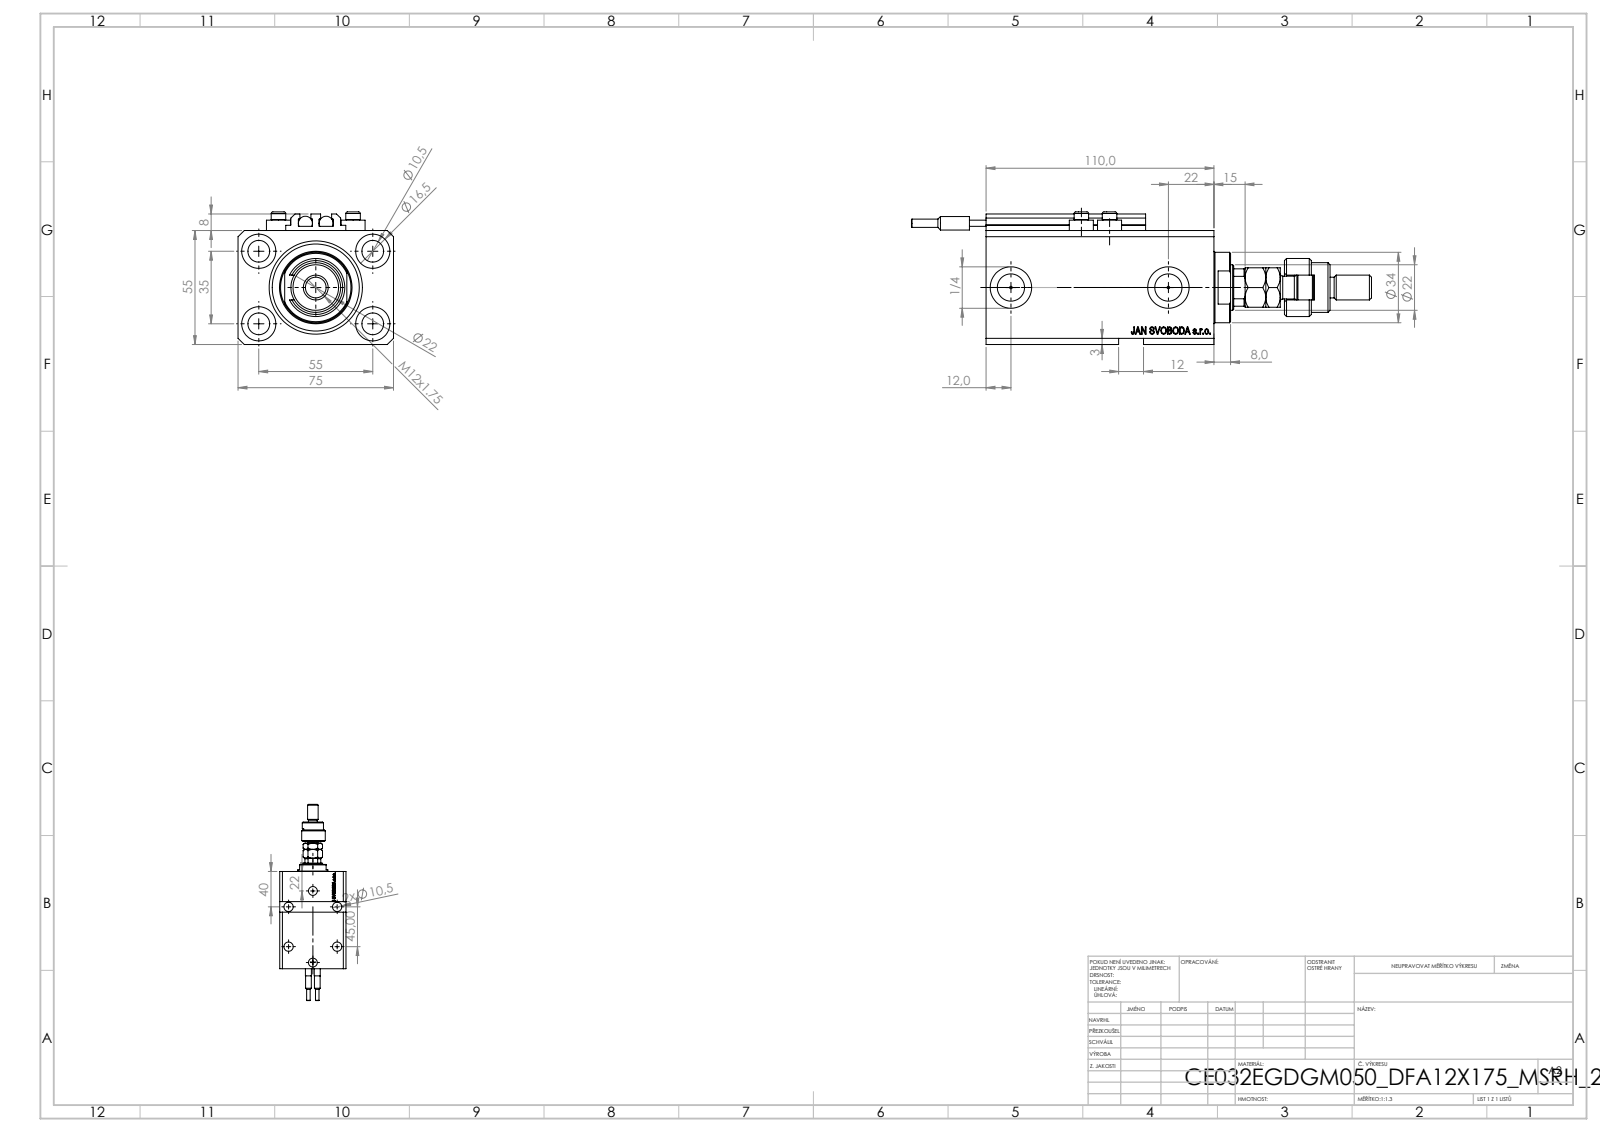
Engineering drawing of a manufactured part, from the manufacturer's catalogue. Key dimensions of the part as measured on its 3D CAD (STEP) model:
Part name (STEP PRODUCT): V250CE_VC_E; FEMALE_PART_FOR_DFA; ALLEN BOLT V250CE; V250CE_C_VCP (+3 more)
STEP written by: SolidWorks 2019 (CONFIG_CONTROL_DESIGN)
Units: millimetres
Bodies: 12 solids, 1237 faces (578 planar, 183 cylindrical, 476 other)
Overall size (bounding box): 222 × 75 × 64
Volume: 399 171 mm³ · Surface area: 106 662 mm²
Round holes (diameter × count): ⌀10.5 ×9, ⌀1.25 ×4, ⌀4 ×4, ⌀16.5 ×4, ⌀10 ×2, ⌀13.16 ×2, ⌀20 ×2, ⌀22 ×1, ⌀32 ×1, ⌀45 ×1
Round bosses / shafts (diameter × count): ⌀11.6 ×4, ⌀7 ×4, ⌀6.8 ×2, ⌀6.5 ×2, ⌀4 ×2, ⌀34 ×1, ⌀28 ×1, ⌀24 ×1
Partial cylindrical surfaces — rounded edges, fillets, slot ends (radius × count): R0.2 ×10, R9.75 ×1, R10.5 ×1
Main face-to-face distances: 55, 75, 15, 3, 110, 57, 95, 9.9, 8, 19
Hole centre spacings: 32.6, 32.87, 55, 68.74, 13.6, 14.09, 23.05, 25.81
